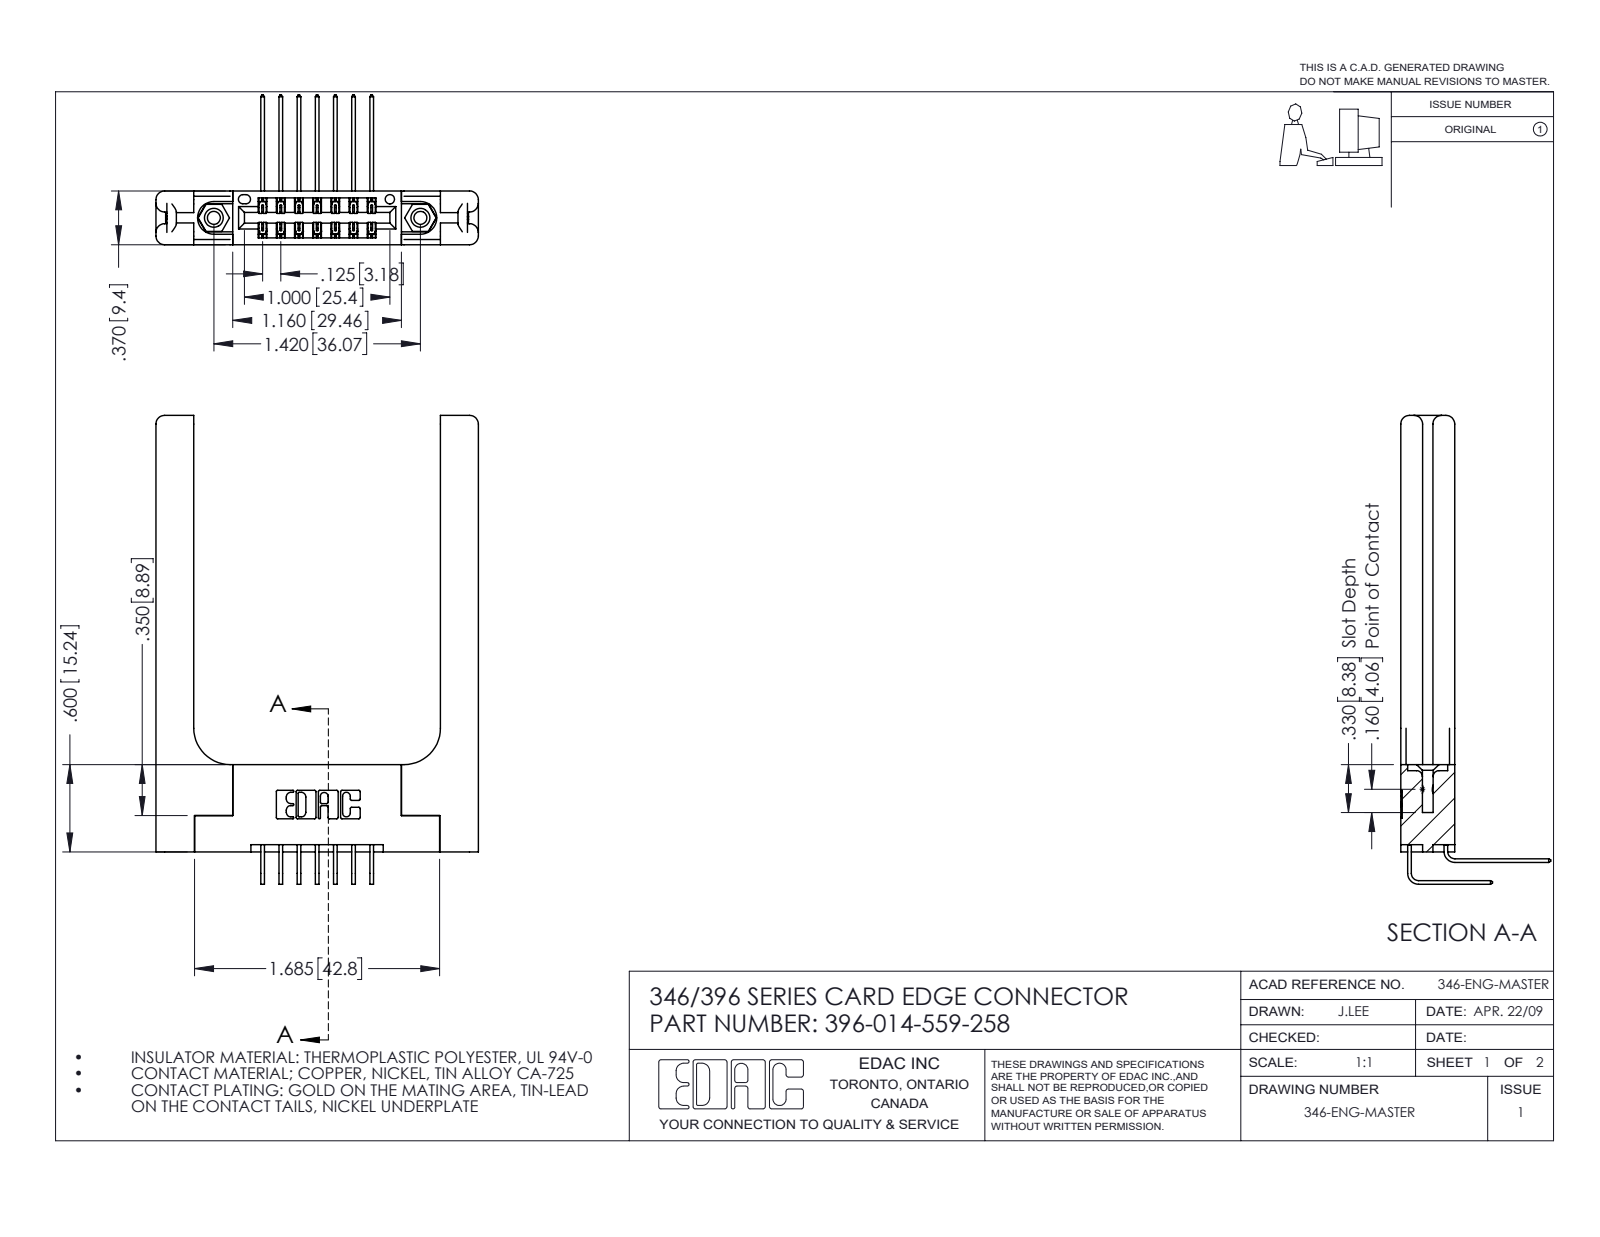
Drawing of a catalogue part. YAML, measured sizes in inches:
part_name: "346-220-058_345-220-058; 345-292-001_559 Tail - 2; 345-292-001_558 559 Tail - 1; 346 Part_Flush Mounting Lugs - 0.156 Dia-TH (+2 more)"
step_written_by: "SolidWorks 2016 (CONFIG_CONTROL_DESIGN)"
units: inches
bodies: {solids: 19, faces: 1134, planar: 742, cylindrical: 332, other: 60}
overall_size: [3.223, 2.216, 1.03]
volume: 0.781
surface_area: 18.74
round_holes:
  - {diameter: 0.089, count: 2}
  - {diameter: 0.125, count: 2}
  - {diameter: 0.156, count: 2}
  - {diameter: 0.064, count: 1}
round_bosses_or_shafts:
  - {diameter: 0.155, count: 2}
partial_cylinders:
  - {radius: 0.01, count: 22}
  - {radius: 0.006, count: 21}
  - {radius: 0.06, count: 16}
  - {radius: 0.007, count: 6}
  - {radius: 0.031, count: 6}
  - {radius: 0.026, count: 3}
  - {radius: 0.014, count: 2}
  - {radius: 0.022, count: 2}
face_to_face_distances: [0.37, 0.15, 0.22, 0.072, 0.25, 0.148, 0.048, 0.322, 0.025, 0.102]
hole_center_spacings: [0.246, 1.217, 1.42]
